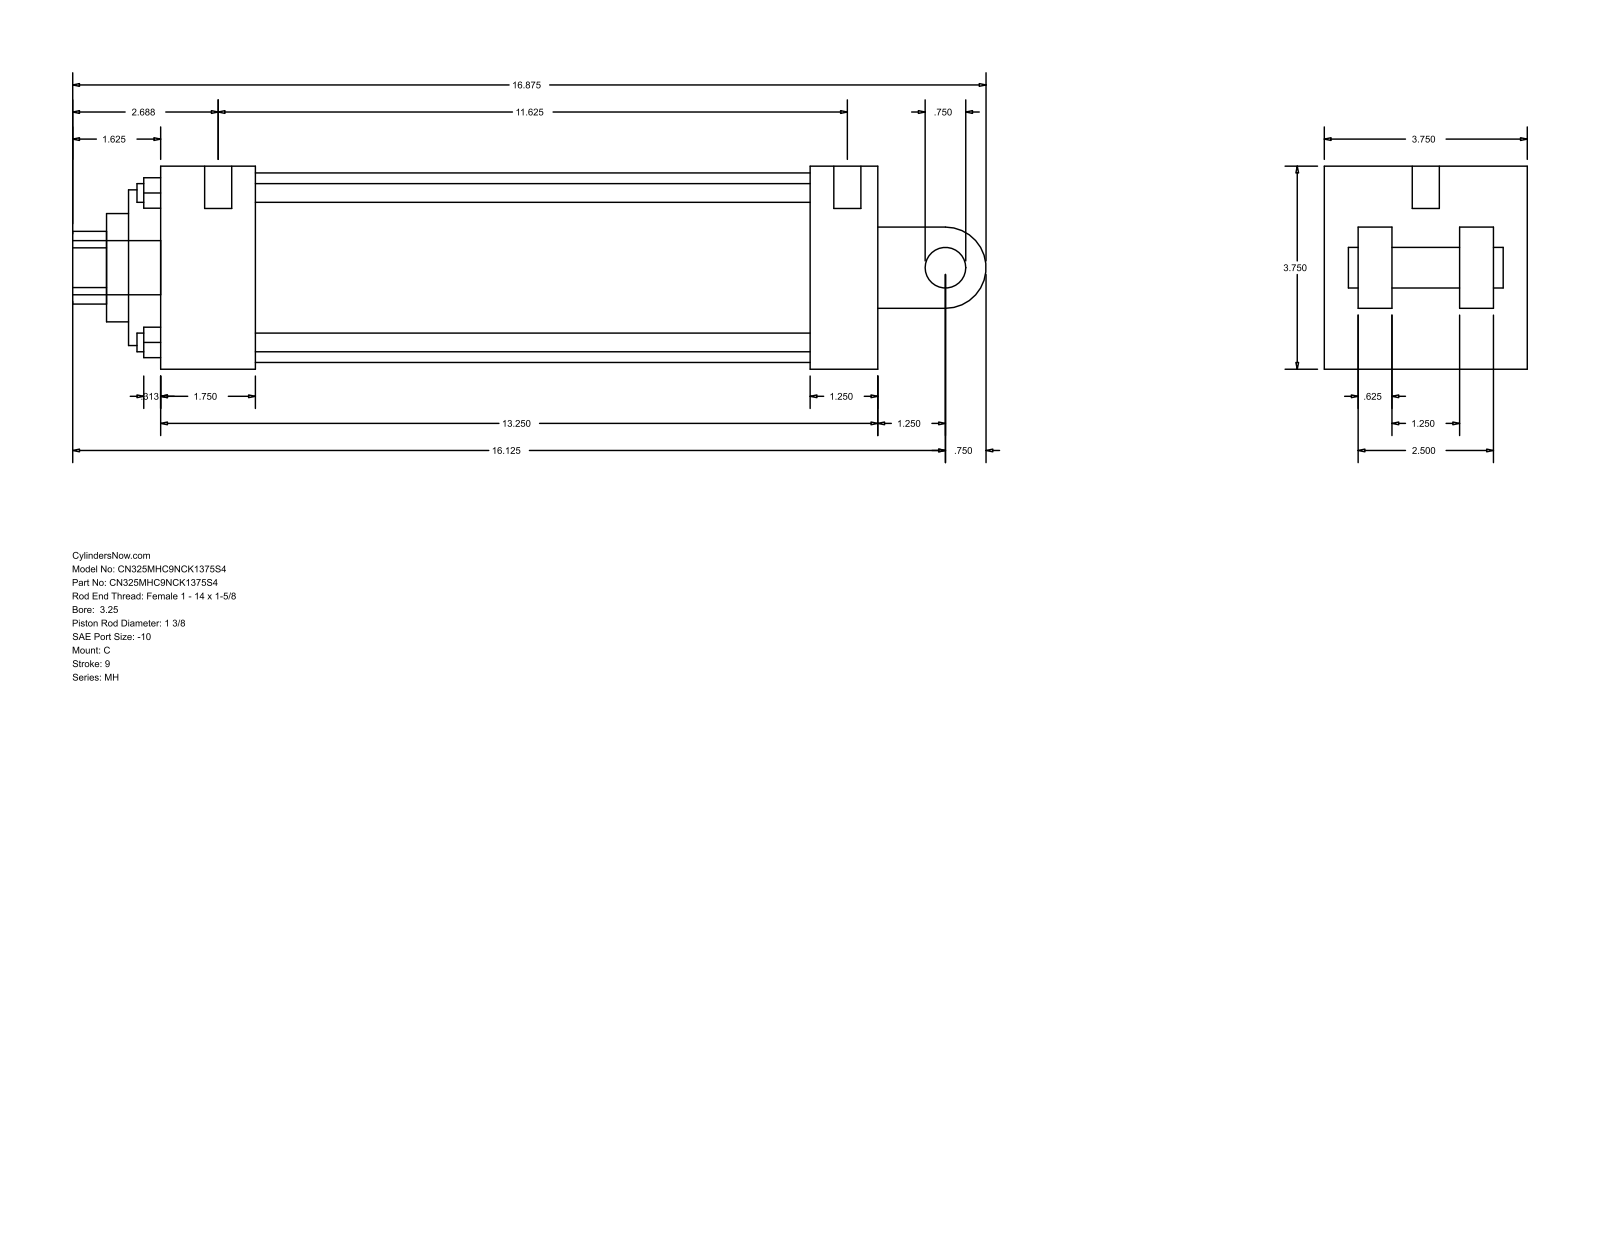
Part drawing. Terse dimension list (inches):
name: MH_C__0325_1.375
written by: GSSL Pune (CONFIG_CONTROL_DESIGN)
unit: in
bodies: 0 solids, 101 faces (71 planar, 30 cylindrical, 0 other)
size: 16.875 × 3.75 × 3.75
holes: 4× ⌀0.345, 2× ⌀0.219, 1× ⌀0.5, 1× ⌀1.375, 1× ⌀2, 1× ⌀2.875, 1× ⌀3.5
bosses: 2× ⌀0.219, 1× ⌀1, 1× ⌀0.75, 1× ⌀0.5
rounds: 1× R0.672, 1× R0.75
face distances: 3.75, 0.625, 13.25, 2.5, 3.125, 1.25, 1.875, 1.75, 12, 10.25
hole spacings: 1.952, 2.76, 3.903, 0.187
